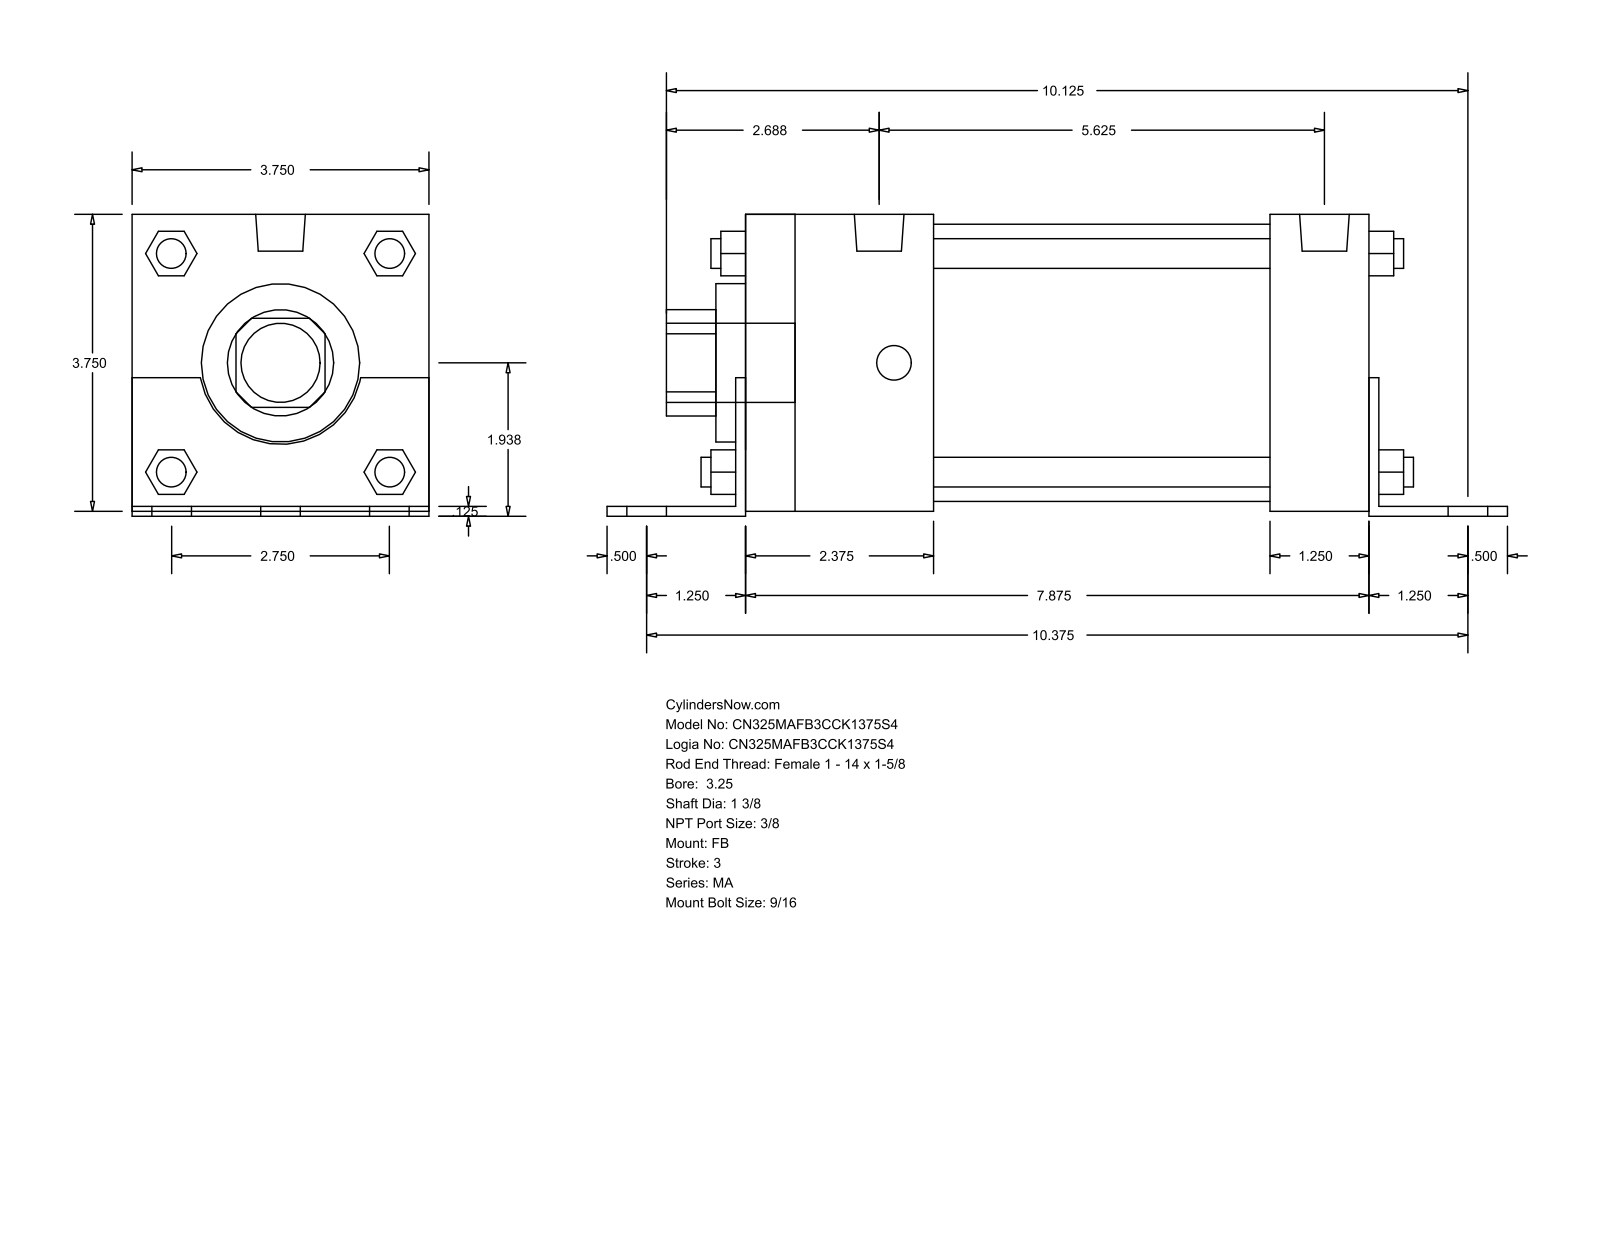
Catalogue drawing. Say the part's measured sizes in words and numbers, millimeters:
The part is named "MA_FB__0325_1.375". Its 3-D file was written by "GSSL Pune (CONFIG_CONTROL_DESIGN)". It is 0 solids with 140 faces: 105 planar, 35 cylindrical and 0 other. Overall it measures 288.93 by 96.84 by 95.25 millimeters. Round holes: 1 of diameter 34.92, 1 of diameter 50.8, 1 of diameter 88.9. Round bosses or shafts: 6 of diameter 14.29, 4 of diameter 11.11, 4 of diameter 9.53, 2 of diameter 15.93, 1 of diameter 25.4. Partial cylindrical surfaces (rounded edges, fillets, slot ends): 1 of radius 17.06, 1 of radius 26.16. The main face-to-face distances are 95.24, 3.17, 1.59, 96.83, 1.58, 93.66, 203.2, 200.03, 31.75, 60.32.
